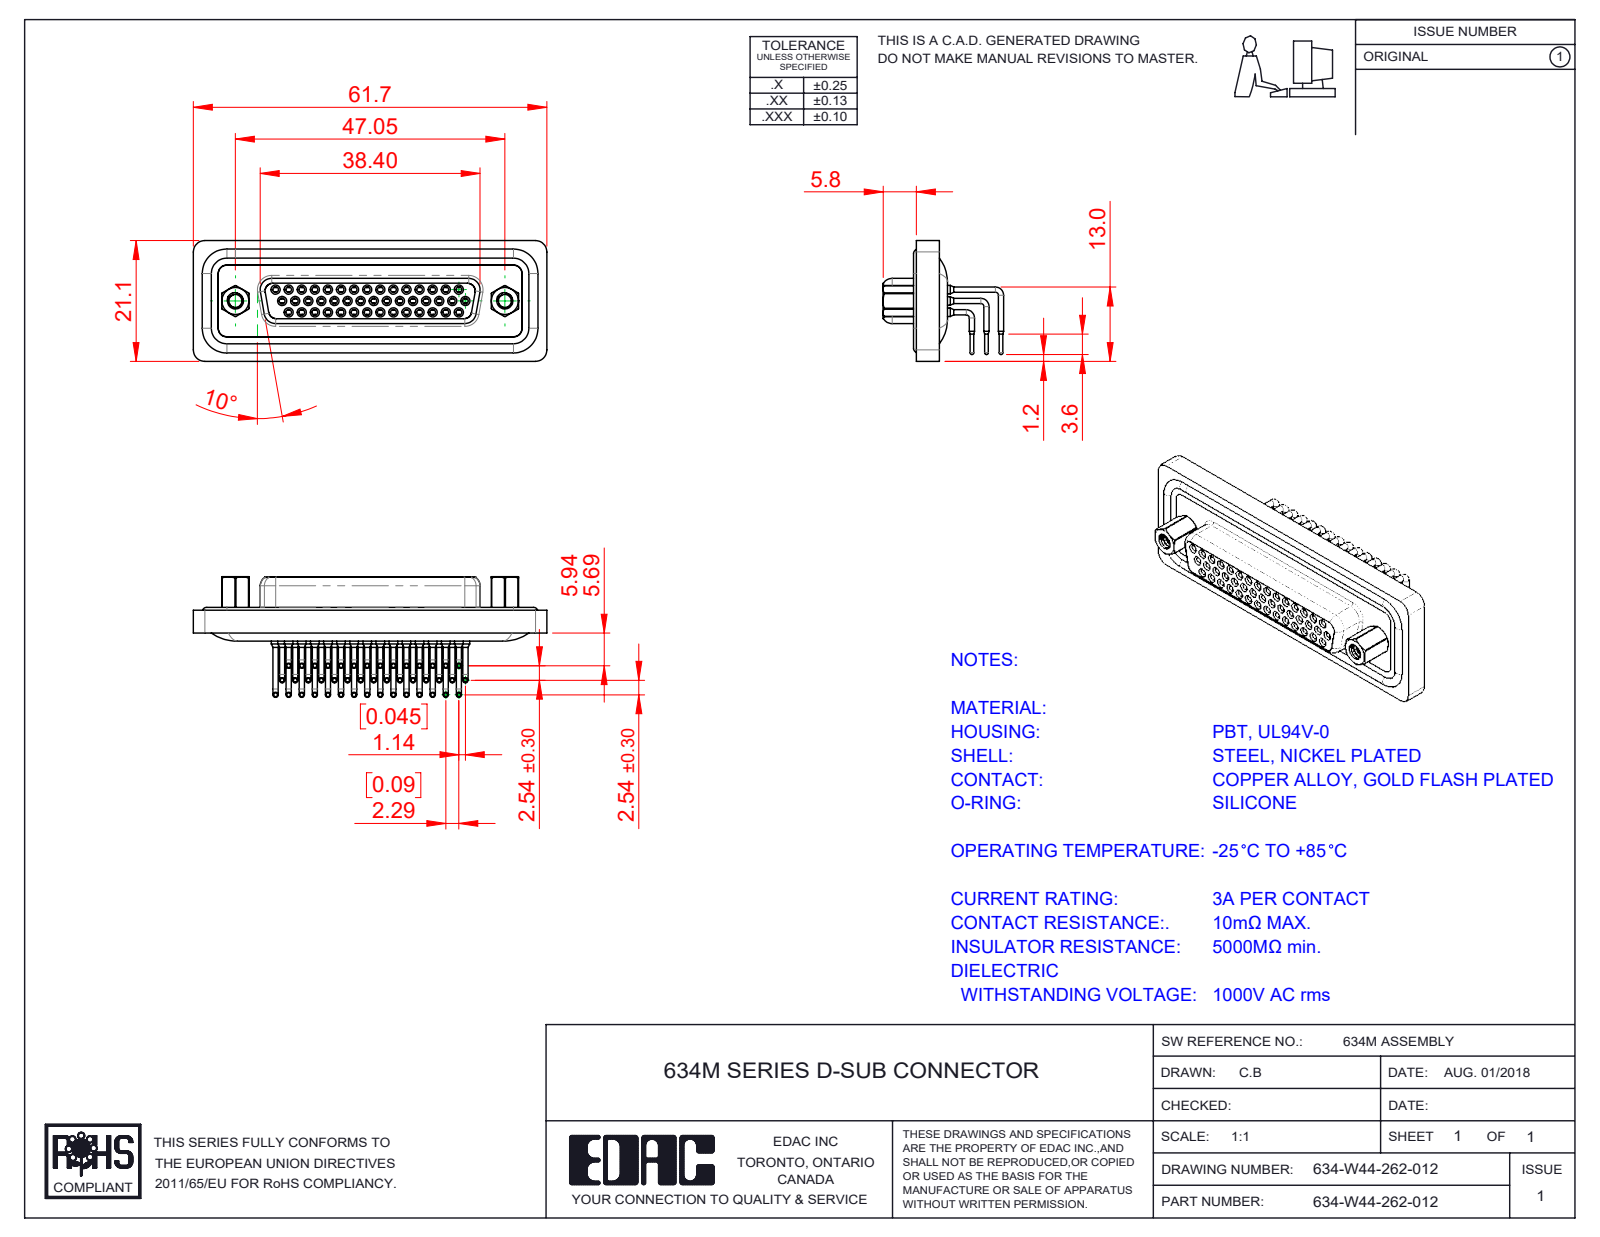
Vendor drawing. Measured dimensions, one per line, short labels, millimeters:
name: 634W 4-40 Hex Standoff; 634W 4-40 Threaded Rivet; 634W Waterproof Housing_44 Contacts; 634W Contact Row 2 (+5 more)
written by: SolidWorks 2016 (CONFIG_CONTROL_DESIGN)
unit: mm
bodies: 52 solids, 2841 faces (761 planar, 1316 cylindrical, 764 other)
size: 61.74 × 21.1 × 21.07
volume: 7 466 mm³; area: 16 704 mm²
holes: 44× ⌀1, 44× ⌀1.1, 44× ⌀1.5, 44× ⌀1.7, 44× ⌀1.8, 44× ⌀2, 2× ⌀2.26, 2× ⌀2.29, 2× ⌀4, 2× ⌀4.8, 2× ⌀5
bosses: 88× ⌀0.9, 48× ⌀1.6, 44× ⌀0.65, 23× ⌀1.5, 2× ⌀4.9, 2× ⌀2.79, 1× ⌀5
rounds: 14× R2, 13× R1.5, 8× R1.35, 6× R2.7, 4× R0.5, 4× R0.9, 4× R1.6, 4× R1.75
face distances: 0.4, 1.8, 1.6, 2.5, 1.1, 2.9, 7.45, 13.65, 5.65, 15.45
hole spacings: 2.28, 3.96, 2.29, 4.57, 8.24, 6.86, 11.43, 10.48
